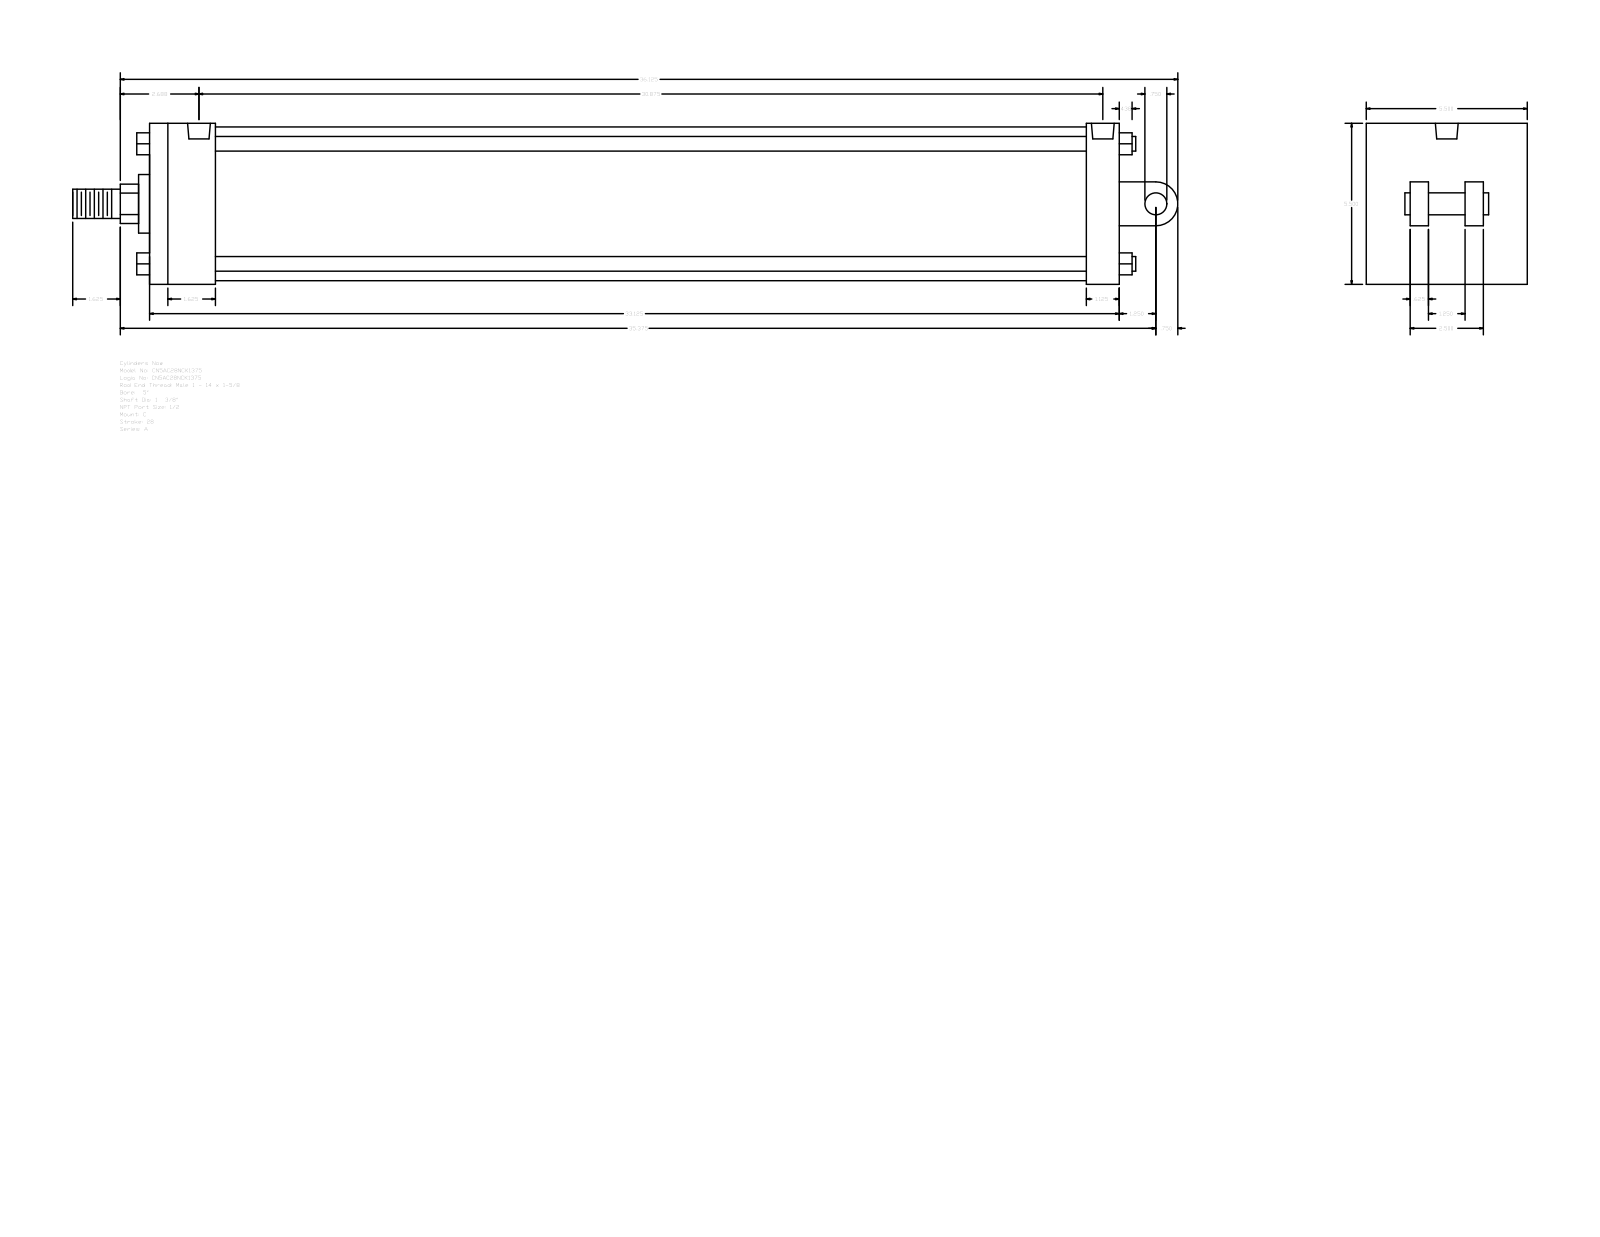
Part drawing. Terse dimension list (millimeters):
name: A_C__0500_1.375
written by: GSSL Pune (CONFIG_CONTROL_DESIGN)
unit: mm
bodies: 0 solids, 135 faces (102 planar, 33 cylindrical, 0 other)
size: 958.85 × 139.7 × 139.7
holes: 4× ⌀8.73, 2× ⌀19.77
bosses: 4× ⌀12.7, 1× ⌀133.35, 1× ⌀50.8, 1× ⌀34.92, 1× ⌀25.4, 1× ⌀19.05
rounds: 1× R17.06, 1× R19.05
face distances: 139.7, 841.37, 57.15, 812.8, 755.65, 784.22, 28.57, 38.1, 53.97, 85.73
hole spacings: 2.39, 779.45, 781.84, 784.23
